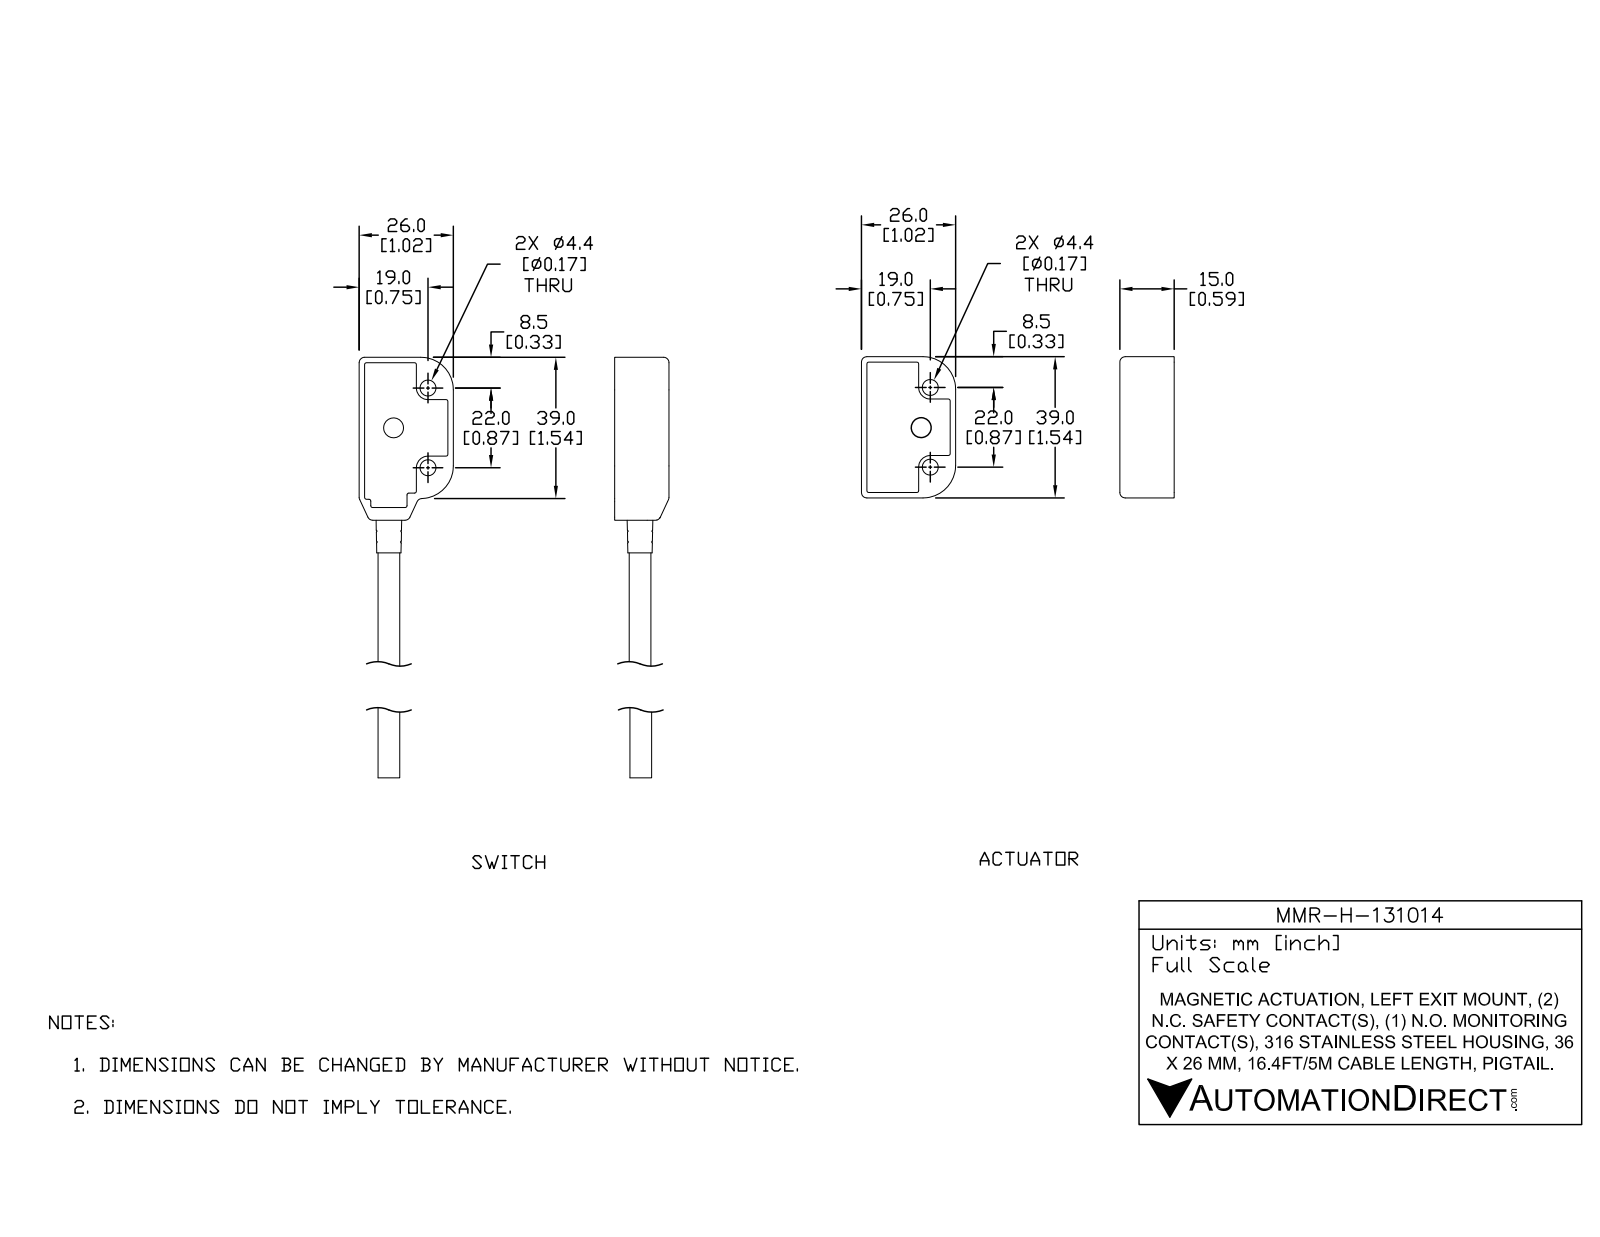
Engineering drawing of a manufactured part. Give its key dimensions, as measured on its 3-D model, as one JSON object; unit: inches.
{"part_name": "MMR-H-131014; MMR-H-131014_1; MMR-H-131014_2", "step_written_by": "SolidWorks 2017 (AUTOMOTIVE_DESIGN)", "units": "inches", "bodies": {"solids": 8, "faces": 590, "planar": 175, "cylindrical": 226, "other": 189}, "overall_size": [7.803, 2.087, 0.591], "volume_in3": 1.231, "surface_area_in2": 30.87, "round_holes": [[0.173, 4], [0.197, 2], [0.118, 1], [0.232, 1], [0.283, 1]], "round_bosses_or_shafts": [[0.079, 2], [0.339, 1], [0.299, 1], [0.28, 1], [0.236, 1]], "partial_cylinders_radius": [[0.02, 83], [0.012, 26], [0.059, 15], [0.008, 8], [0.157, 6], [0.126, 4], [0.13, 4], [0.181, 4]], "face_to_face_distances": [0.059, 0.575, 0.516, 0.098, 0.461, 0.52, 0.055, 0.591, 0.531, 0.965], "hole_center_spacings": [0.572, 0.866, 1.239, 1.535, 1.763, 0.076, 0.44, 0.448]}
